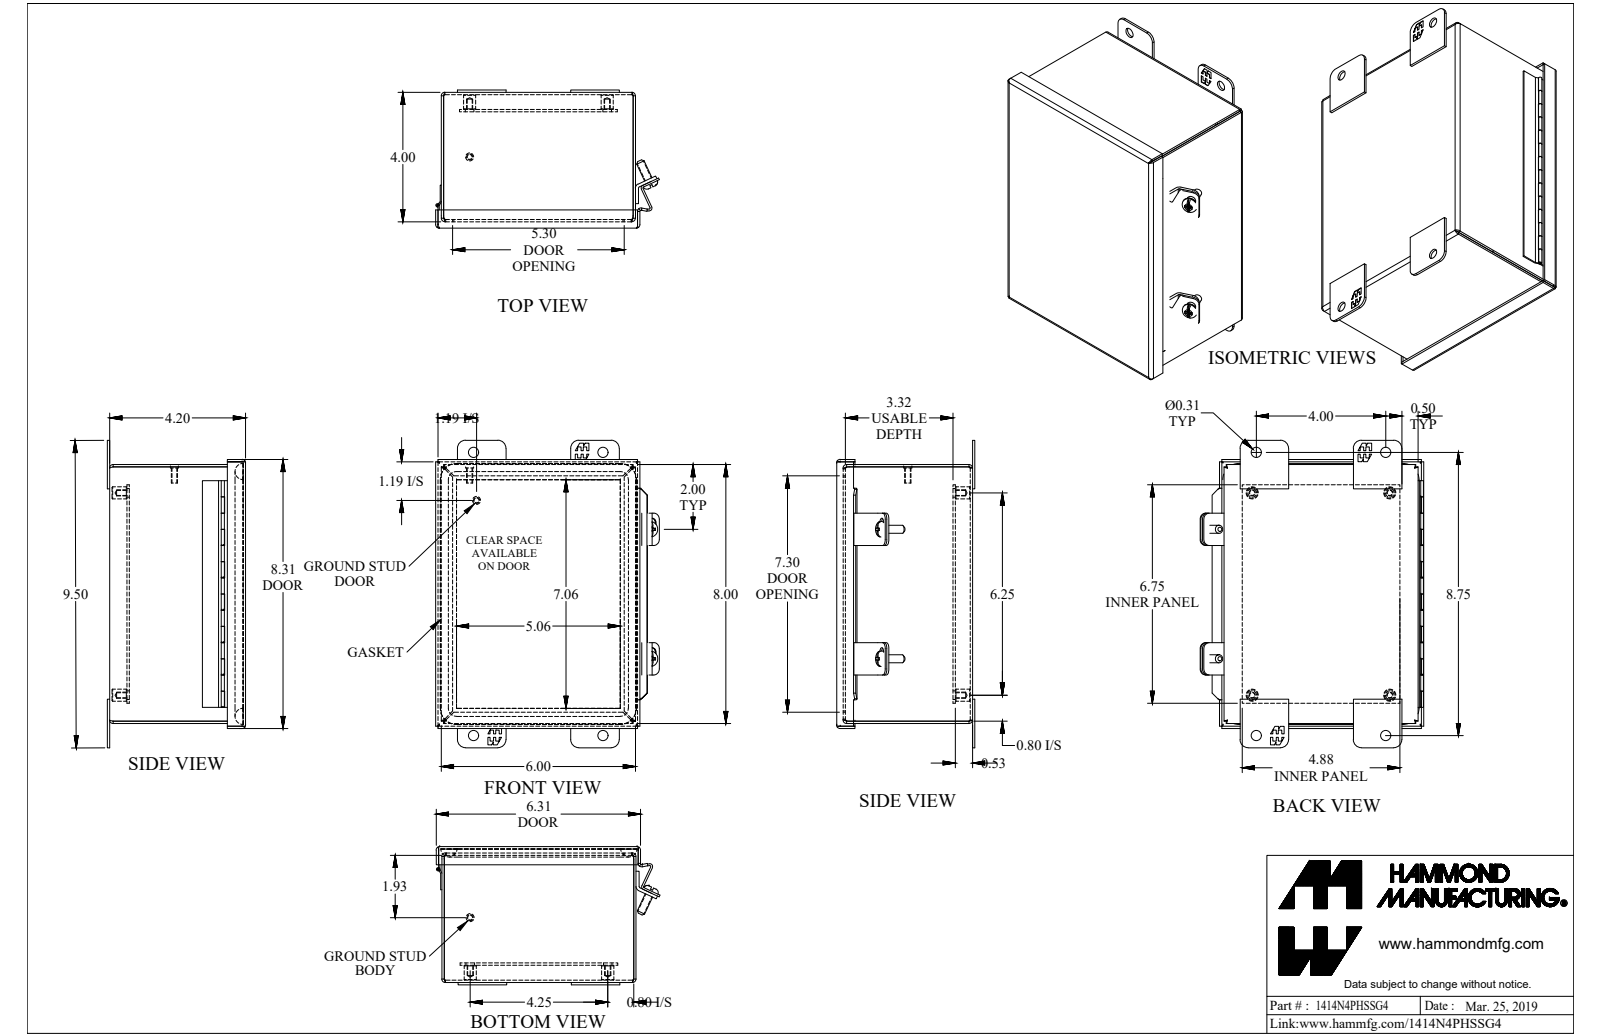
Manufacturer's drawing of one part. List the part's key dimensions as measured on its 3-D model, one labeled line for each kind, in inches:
Part name (STEP PRODUCT): 1414N4PHSSG4
STEP written by: SolidWorks 2018 (AUTOMOTIVE_DESIGN)
Units: inches
Bodies: 21 solids, 668 faces (432 planar, 172 cylindrical, 64 other)
Overall size (bounding box): 9.5 × 6.903 × 4.269
Volume: 22.97 in³ · Surface area: 648.8 in²
Round holes (diameter × count): ⌀0.156 ×4, ⌀0.265 ×4, ⌀0.313 ×4, ⌀0.213 ×2, ⌀0.05 ×1
Round bosses / shafts (diameter × count): ⌀0.375 ×4, ⌀0.25 ×4, ⌀0.48 ×2, ⌀0.19 ×2, ⌀0.1 ×1, ⌀0.045 ×1
Partial cylindrical surfaces — rounded edges, fillets, slot ends (radius × count): R0.25 ×24, R0.036 ×9, R0.108 ×9, R0.188 ×8, R0.007 ×4, R0.01 ×4, R0.046 ×4, R0.079 ×4
Main face-to-face distances: 0.072, 4.125, 3.593, 0.532, 5.928, 4.197, 4.053, 7.928, 0.604, 3.665
Hole centre spacings: 1.256, 7.501, 8.559, 6.25, 4.31, 7.558, 4, 4.25
